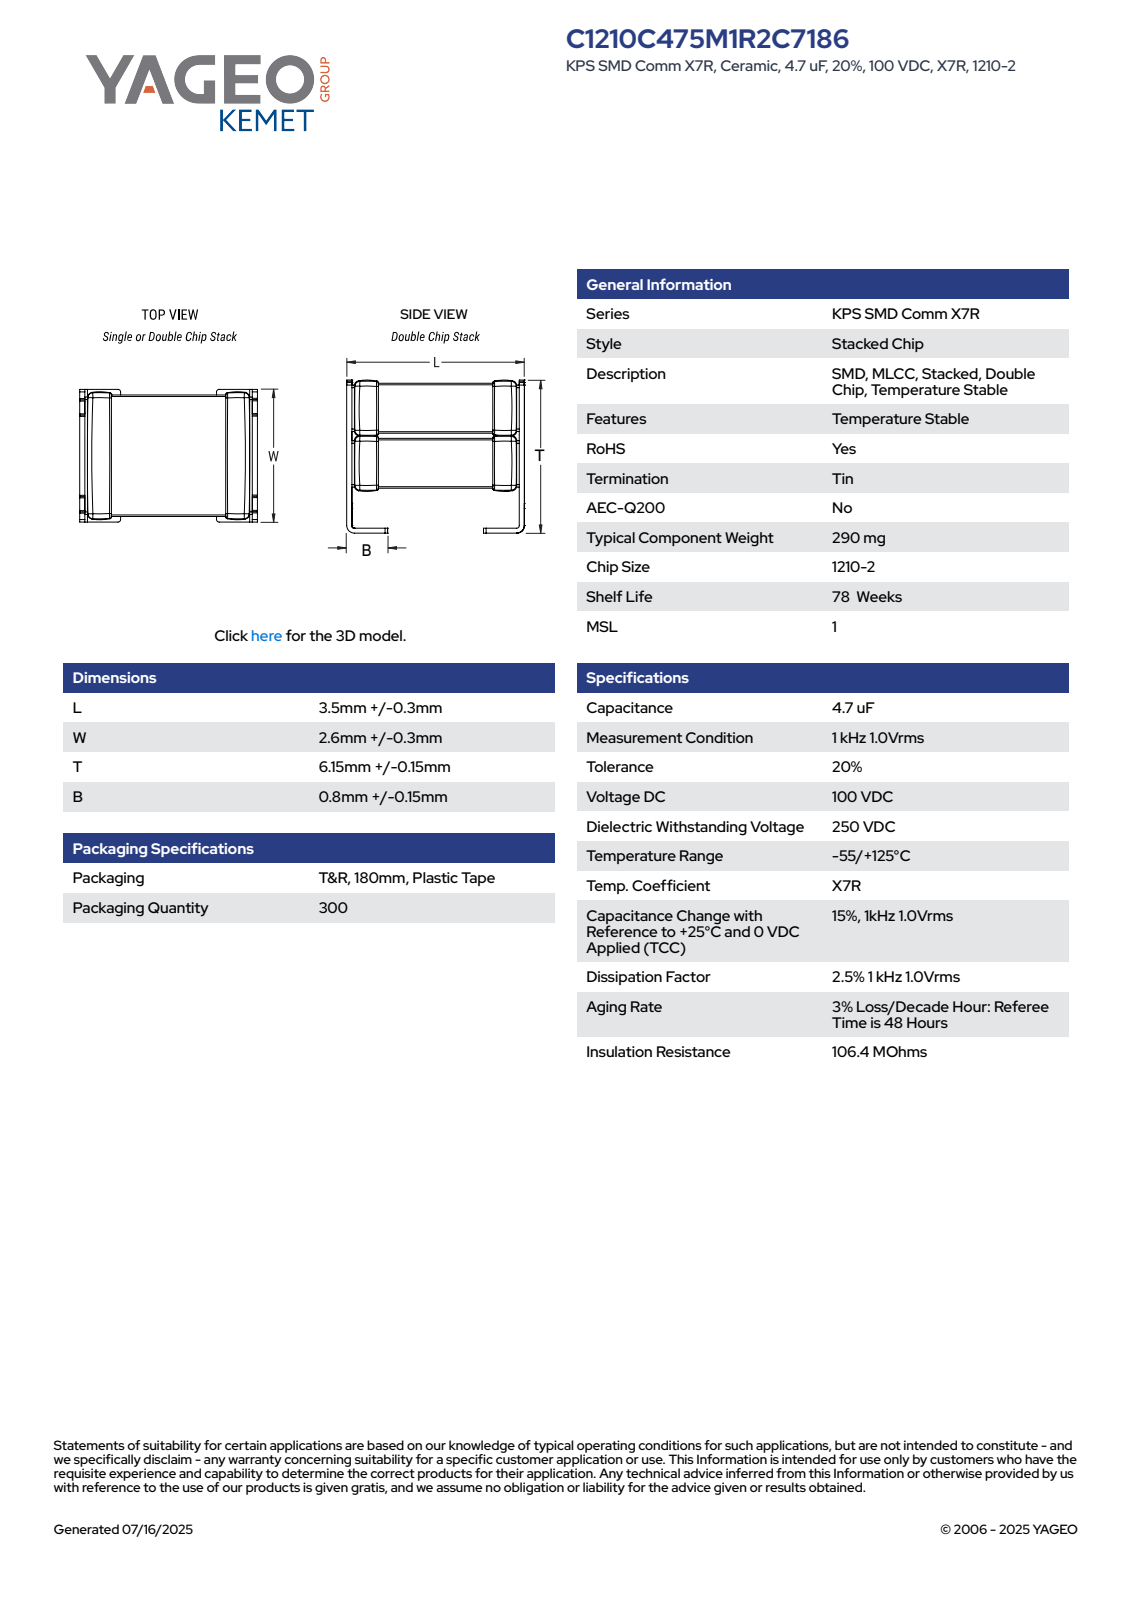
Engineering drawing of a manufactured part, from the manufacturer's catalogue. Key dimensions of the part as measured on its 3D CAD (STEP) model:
Part name (STEP PRODUCT): CCSS_S2_1210-2_L3.8W2.9T6.3B0.95
STEP written by: SolidWorks 2014 (AUTOMOTIVE_DESIGN)
Units: millimetres
Bodies: 4 solids, 113 faces (109 planar, 4 cylindrical, 0 other)
Overall size (bounding box): 6.3 × 3.8 × 2.9
Volume: 44 mm³ · Surface area: 135 mm²
Main face-to-face distances: 3.8, 3.7, 2.85, 1.95, 3.95, 1.9, 2.05, 2, 4.25, 2.9
